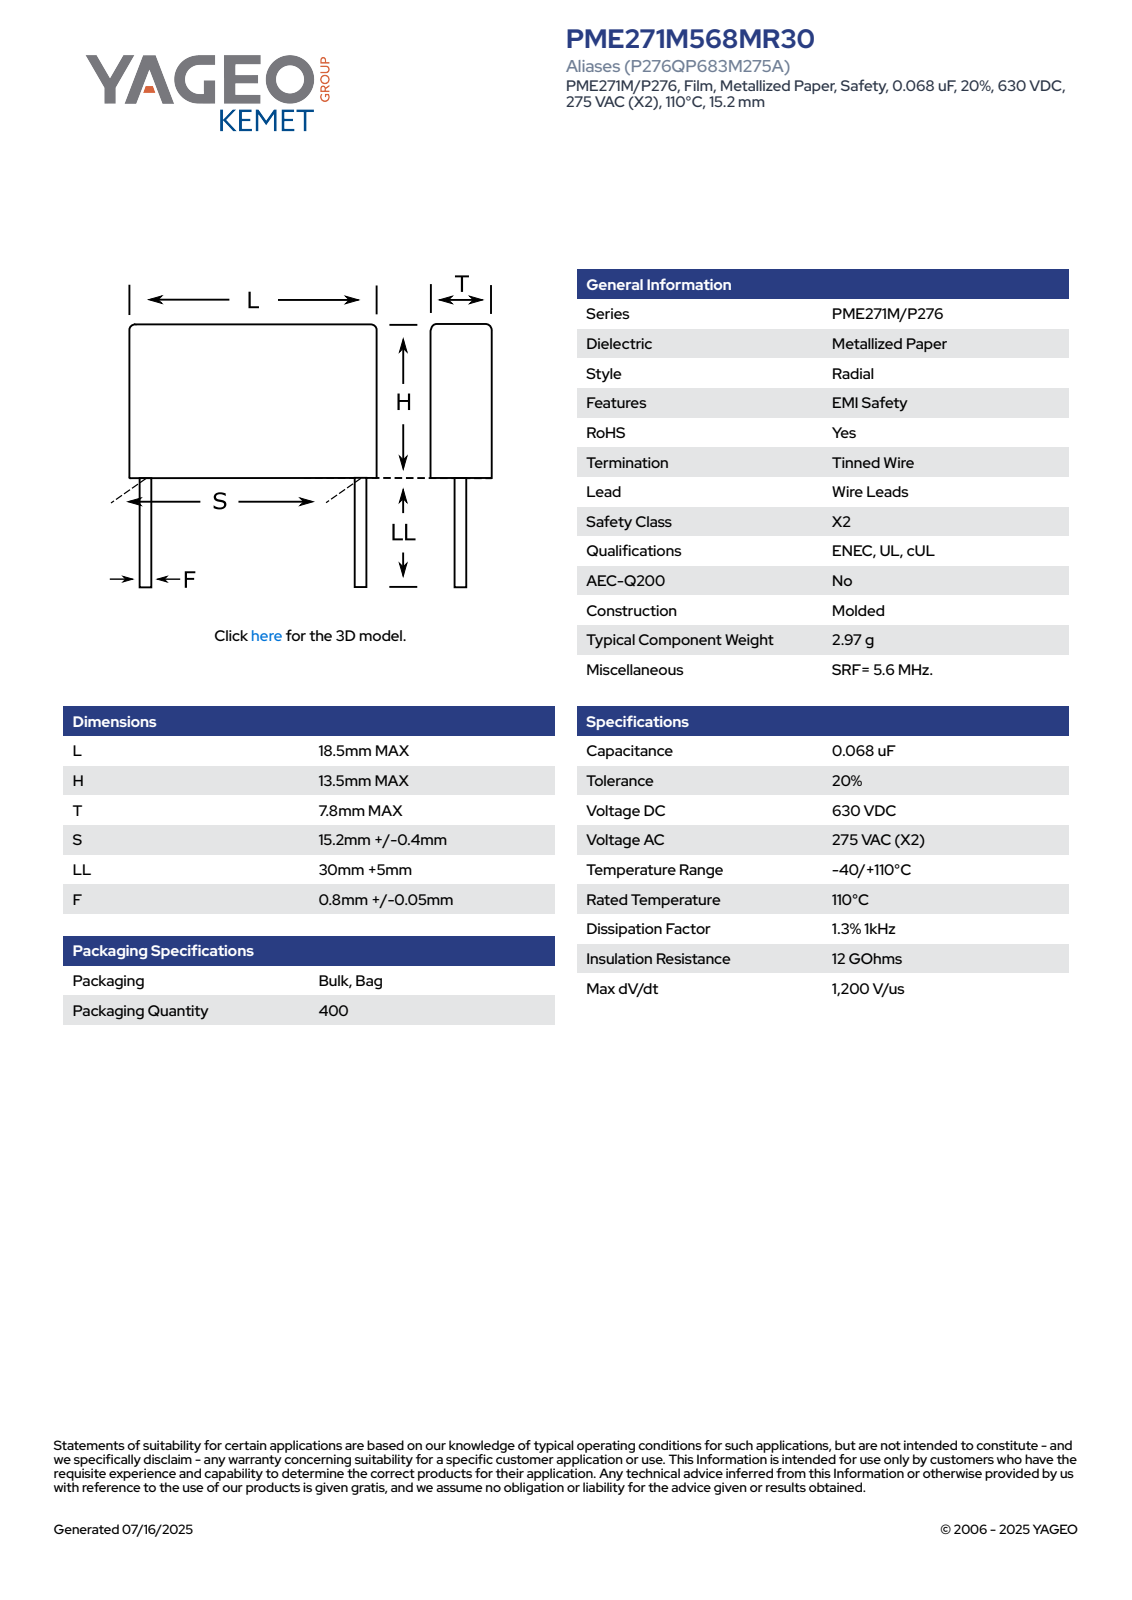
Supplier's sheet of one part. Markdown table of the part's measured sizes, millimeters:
| quantity | value |
| --- | --- |
| part name | CFR_MOLDED_18.5X13.5X7.8_L18.5H13.5T7.8S15.2LL35F0.8 |
| STEP written by | SolidWorks 2014 (AUTOMOTIVE_DESIGN) |
| units | millimeters |
| bodies | 4 solids, 73 faces (65 planar, 8 cylindrical, 0 other) |
| overall size | 48.5 × 18.5 × 7.8 |
| volume | 1 981 mm³ |
| surface area | 1 180 mm² |
| round bosses / shafts (diameter × count) | 0.8 × 2 |
| partial cylindrical surfaces (radius × count) | 0.5 × 4 |
| main face-to-face distances | 7.8, 13.5, 18.5, 35, 48.5, 1.66, 42.32, 7.32, 6.18, 40.66 |
